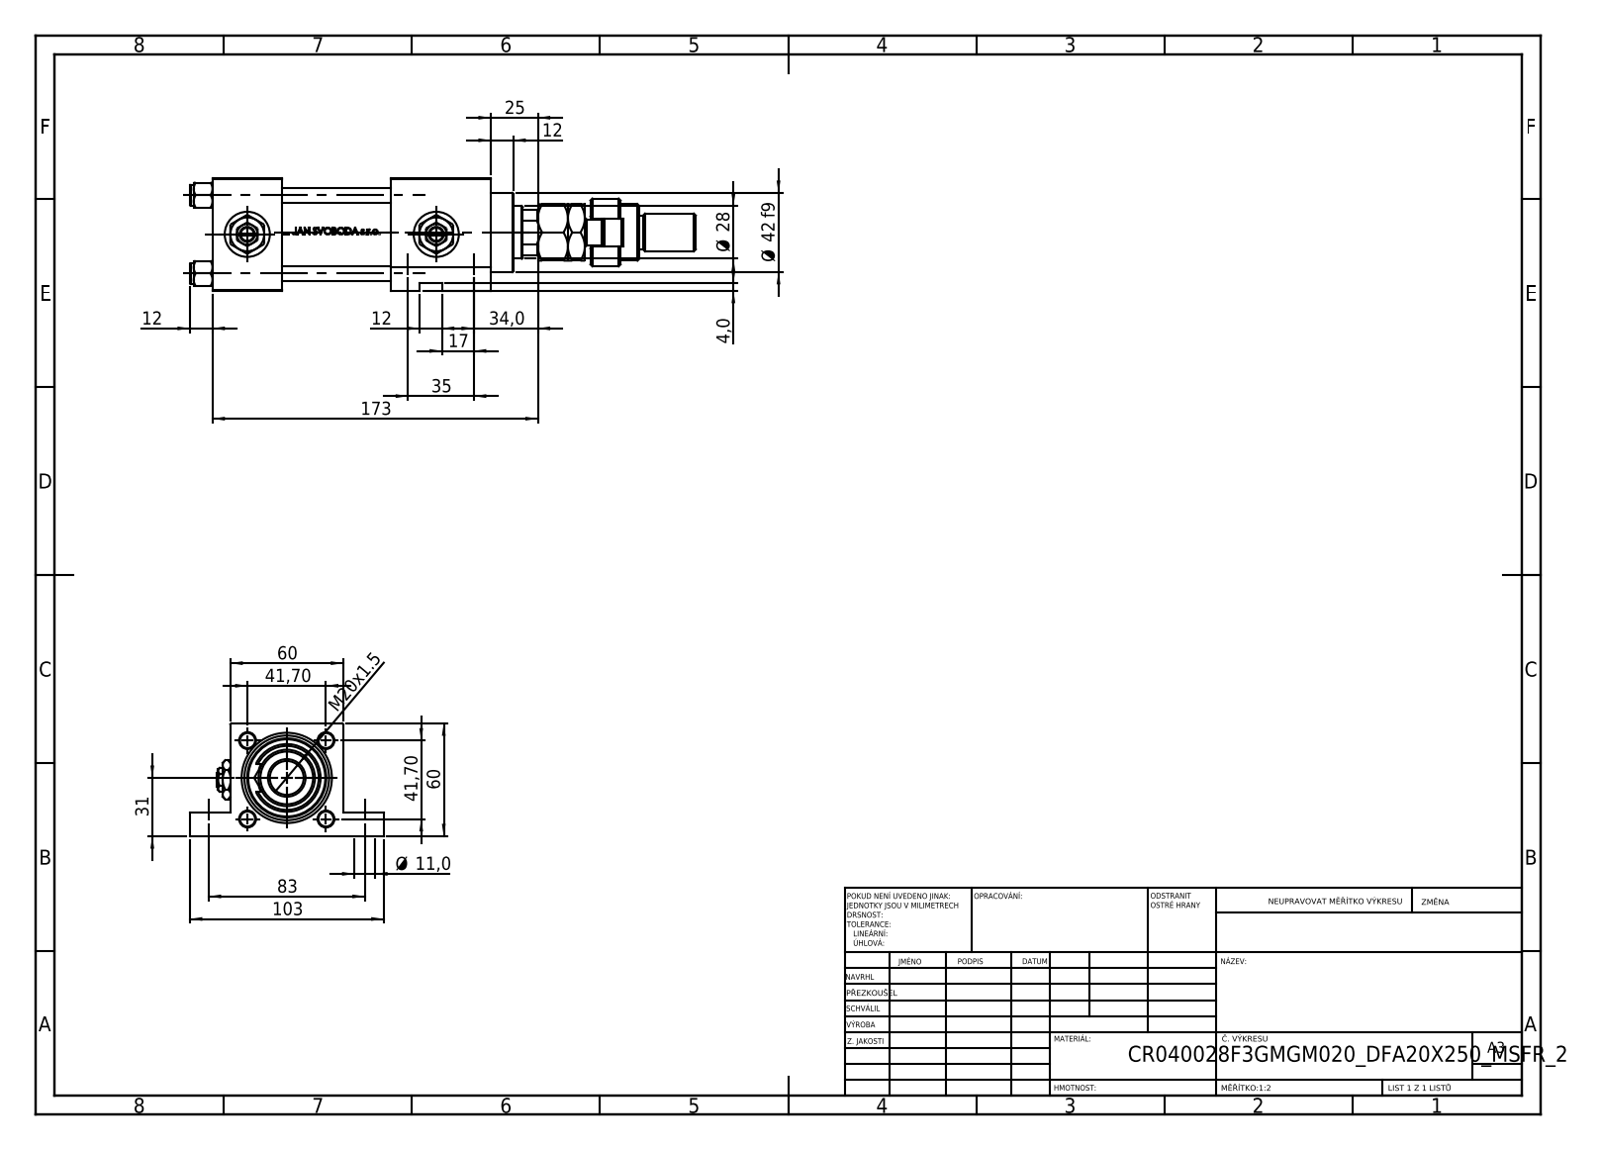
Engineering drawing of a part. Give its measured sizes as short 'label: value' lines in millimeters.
name: Zatka_pro_OIL_PORT; NUT_M5_F; V215CR_F_Body; MFA (+4 more)
written by: SolidWorks 2019 (CONFIG_CONTROL_DESIGN)
unit: mm
bodies: 15 solids, 1300 faces (512 planar, 162 cylindrical, 626 other)
size: 269 × 103 × 60
volume: 490 680 mm³; area: 133 868 mm²
holes: 4× ⌀8, 3× ⌀16.66, 3× ⌀24, 2× ⌀7, 2× ⌀11, 2× ⌀11, 1× ⌀16, 1× ⌀18.5, 1× ⌀28, 1× ⌀31, 1× ⌀40, 1× ⌀45
bosses: 4× ⌀11, 1× ⌀46, 1× ⌀42, 1× ⌀36, 1× ⌀30, 1× ⌀22, 1× ⌀20, 1× ⌀18
rounds: 1× R7.5, 1× R12, 1× R13.5
face distances: 60, 37, 58, 95, 53, 148, 38, 111, 12.5, 47.5
hole spacings: 41.7, 28.79, 30.2, 35, 58.97, 83, 90.08, 8
